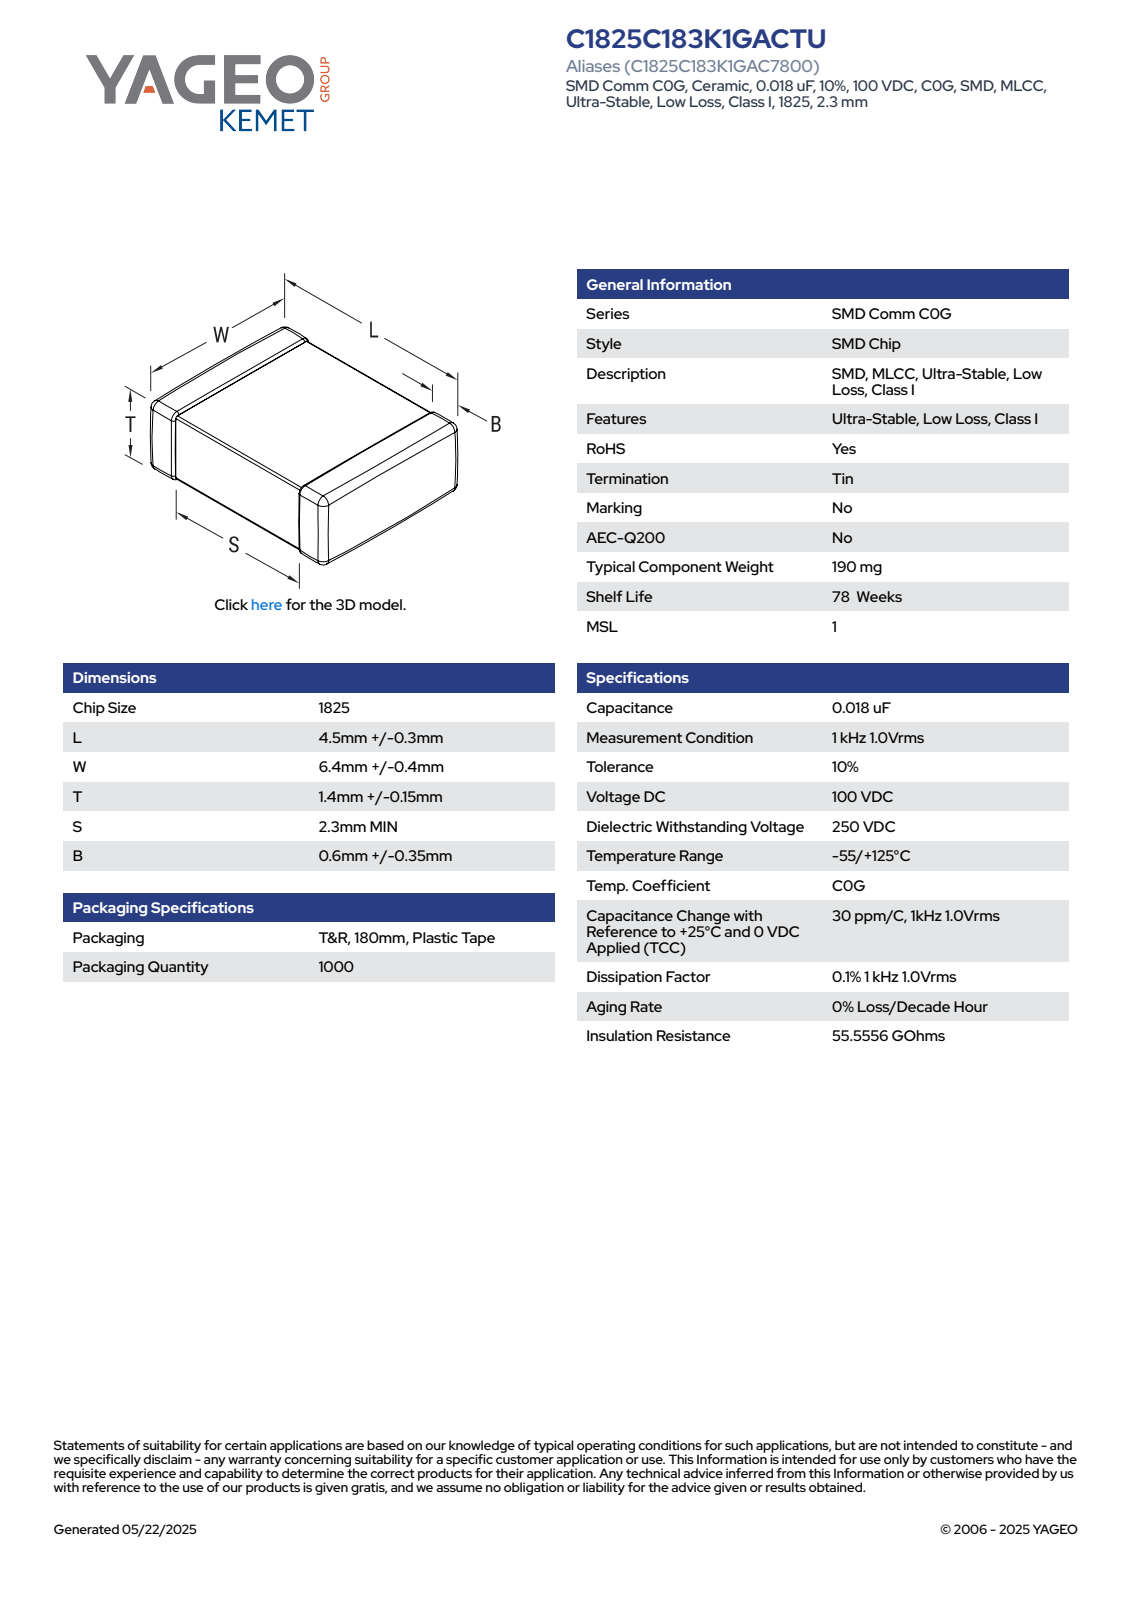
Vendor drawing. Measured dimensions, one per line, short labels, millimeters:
name: CCS_CCSTD_1825_L4.8W6.8T1.55B0.6
written by: SolidWorks 2021 (AUTOMOTIVE_DESIGN)
unit: mm
bodies: 4 solids, 125 faces (71 planar, 38 cylindrical, 16 other)
size: 6.8 × 4.8 × 1.55
volume: 44 mm³; area: 103 mm²
rounds: 24× R0.14
face distances: 1.27, 1.41, 1.55, 4.8, 6.66, 6.52, 6.8, 1.59, 3.21, 2.59
